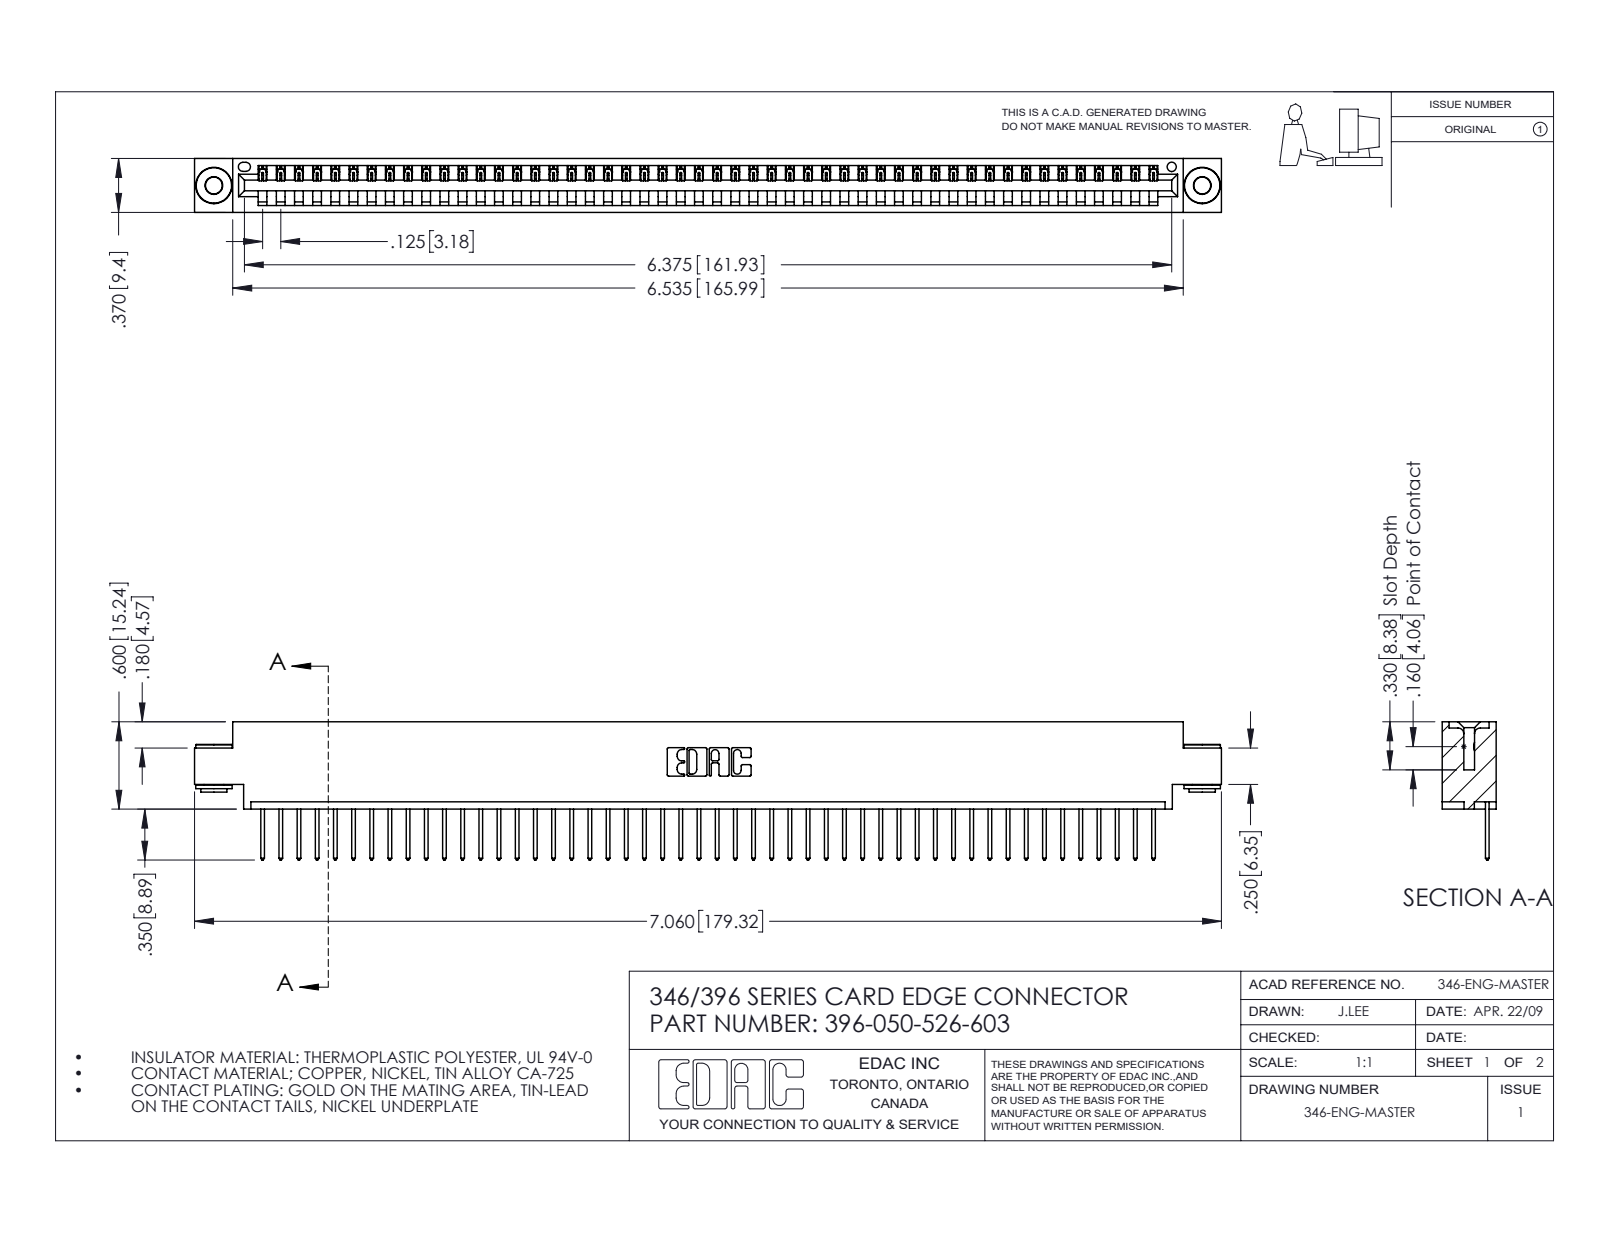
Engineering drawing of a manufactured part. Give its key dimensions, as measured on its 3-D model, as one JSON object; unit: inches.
{"part_name": "345-292-001_345-293-126; 396-050-526-603; 346 Part_0.170 Offset - 0.156 Dia-TH; 345-250-002_345-250-002-102", "step_written_by": "SolidWorks 2016 (CONFIG_CONTROL_DESIGN)", "units": "inches", "bodies": {"solids": 53, "faces": 3064, "planar": 2090, "cylindrical": 966, "other": 8}, "overall_size": [7.06, 0.95, 0.37], "volume_in3": 1.04, "surface_area_in2": 33.67, "round_holes": [[0.116, 2], [0.156, 2], [0.064, 1]], "round_bosses_or_shafts": [[0.25, 2], [0.18, 2], [0.136, 2]], "partial_cylinders_radius": [[0.006, 100], [0.01, 100], [0.01, 22], [0.007, 6], [0.031, 6], [0.026, 3], [0.031, 2], [0.04, 2]], "face_to_face_distances": [0.048, 0.322, 0.37, 0.25, 0.025, 0.072, 0.298, 0.148, 0.222, 0.1], "hole_center_spacings": [0.246, 6.586, 6.795]}
